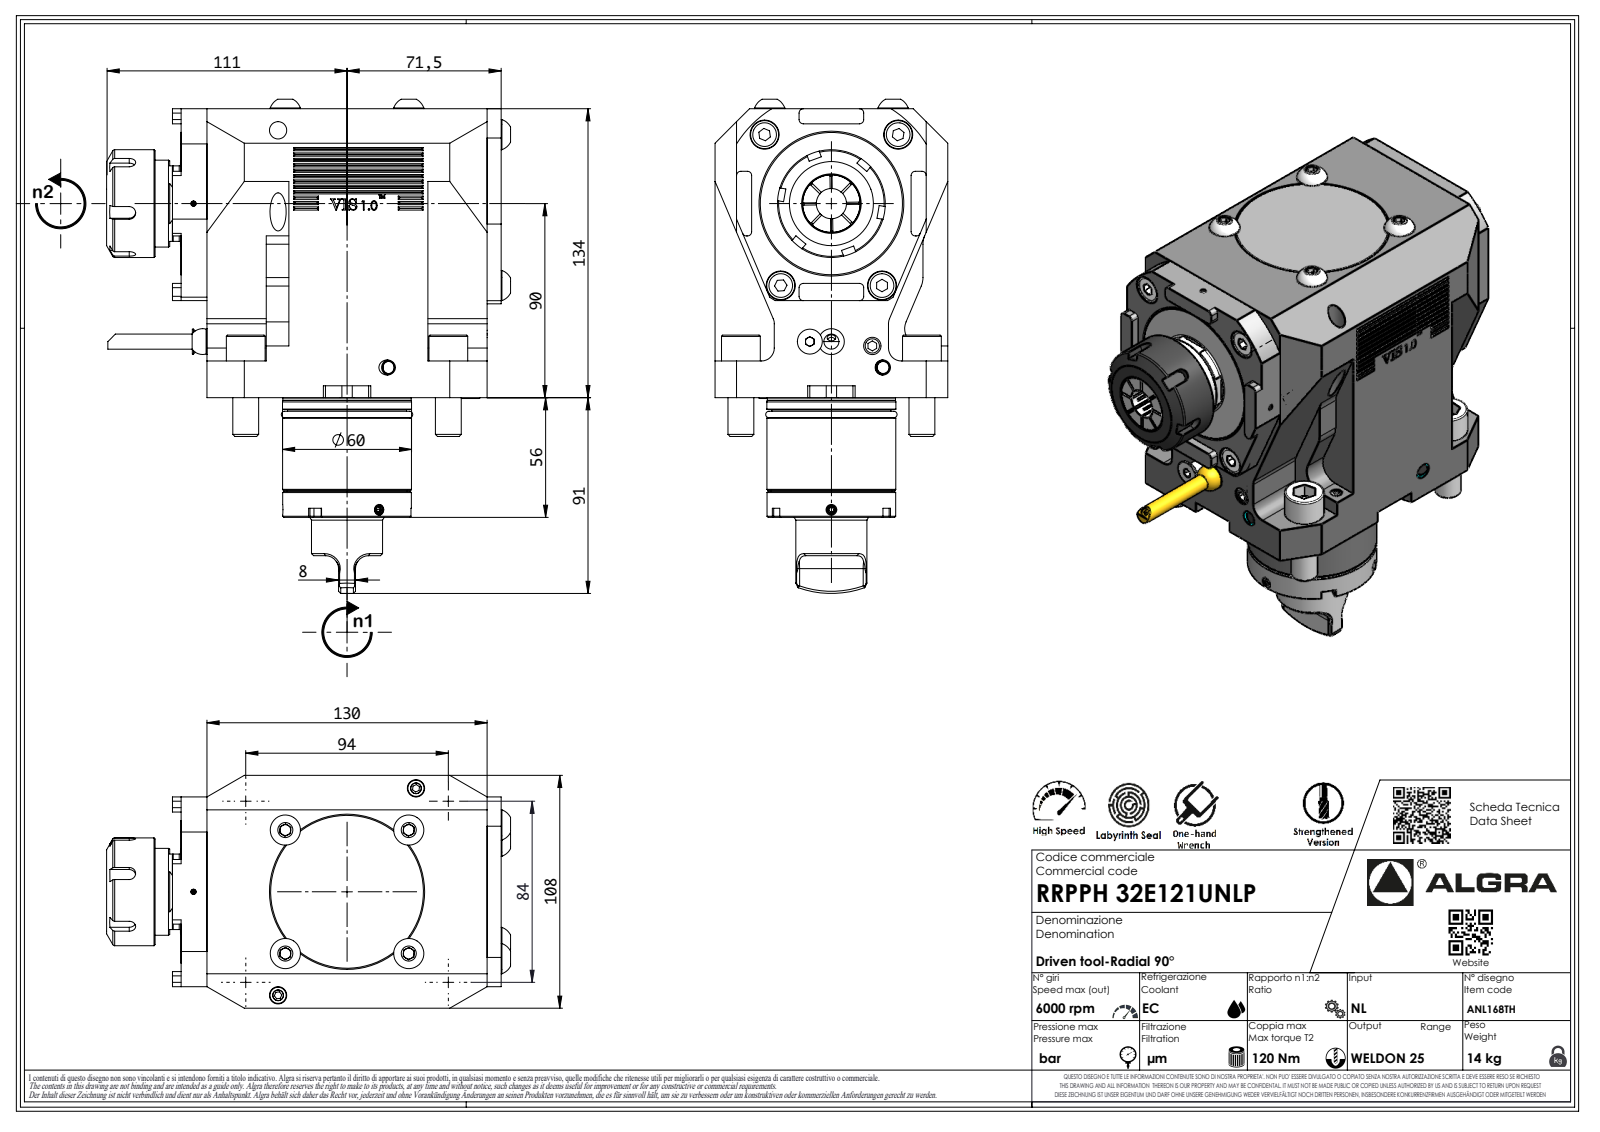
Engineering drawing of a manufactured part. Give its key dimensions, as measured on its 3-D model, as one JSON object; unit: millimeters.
{"part_name": "RRPPH32E121UNLP", "step_written_by": "SolidWorks 2023 (AUTOMOTIVE_DESIGN)", "units": "millimeters", "bodies": {"solids": 1, "faces": 1008, "planar": 678, "cylindrical": 137, "other": 193}, "overall_size": [224.8, 183.09, 108], "volume_mm3": 2034000, "surface_area_mm2": 128455, "round_holes": [[2.1, 1]], "round_bosses_or_shafts": [[18, 4], [12, 4], [59.9, 1], [59.8, 1], [59.7, 1], [59.5, 1], [55.2, 1], [50, 1]], "partial_cylinders_radius": [[0.2, 21], [8, 18], [2, 16], [6, 10], [3, 9], [0.33, 7], [0.52, 7], [3.7, 7]], "face_to_face_distances": [108, 134, 27.5, 12, 102.5, 6.5, 136.5, 5.5, 148.5, 39.5]}
